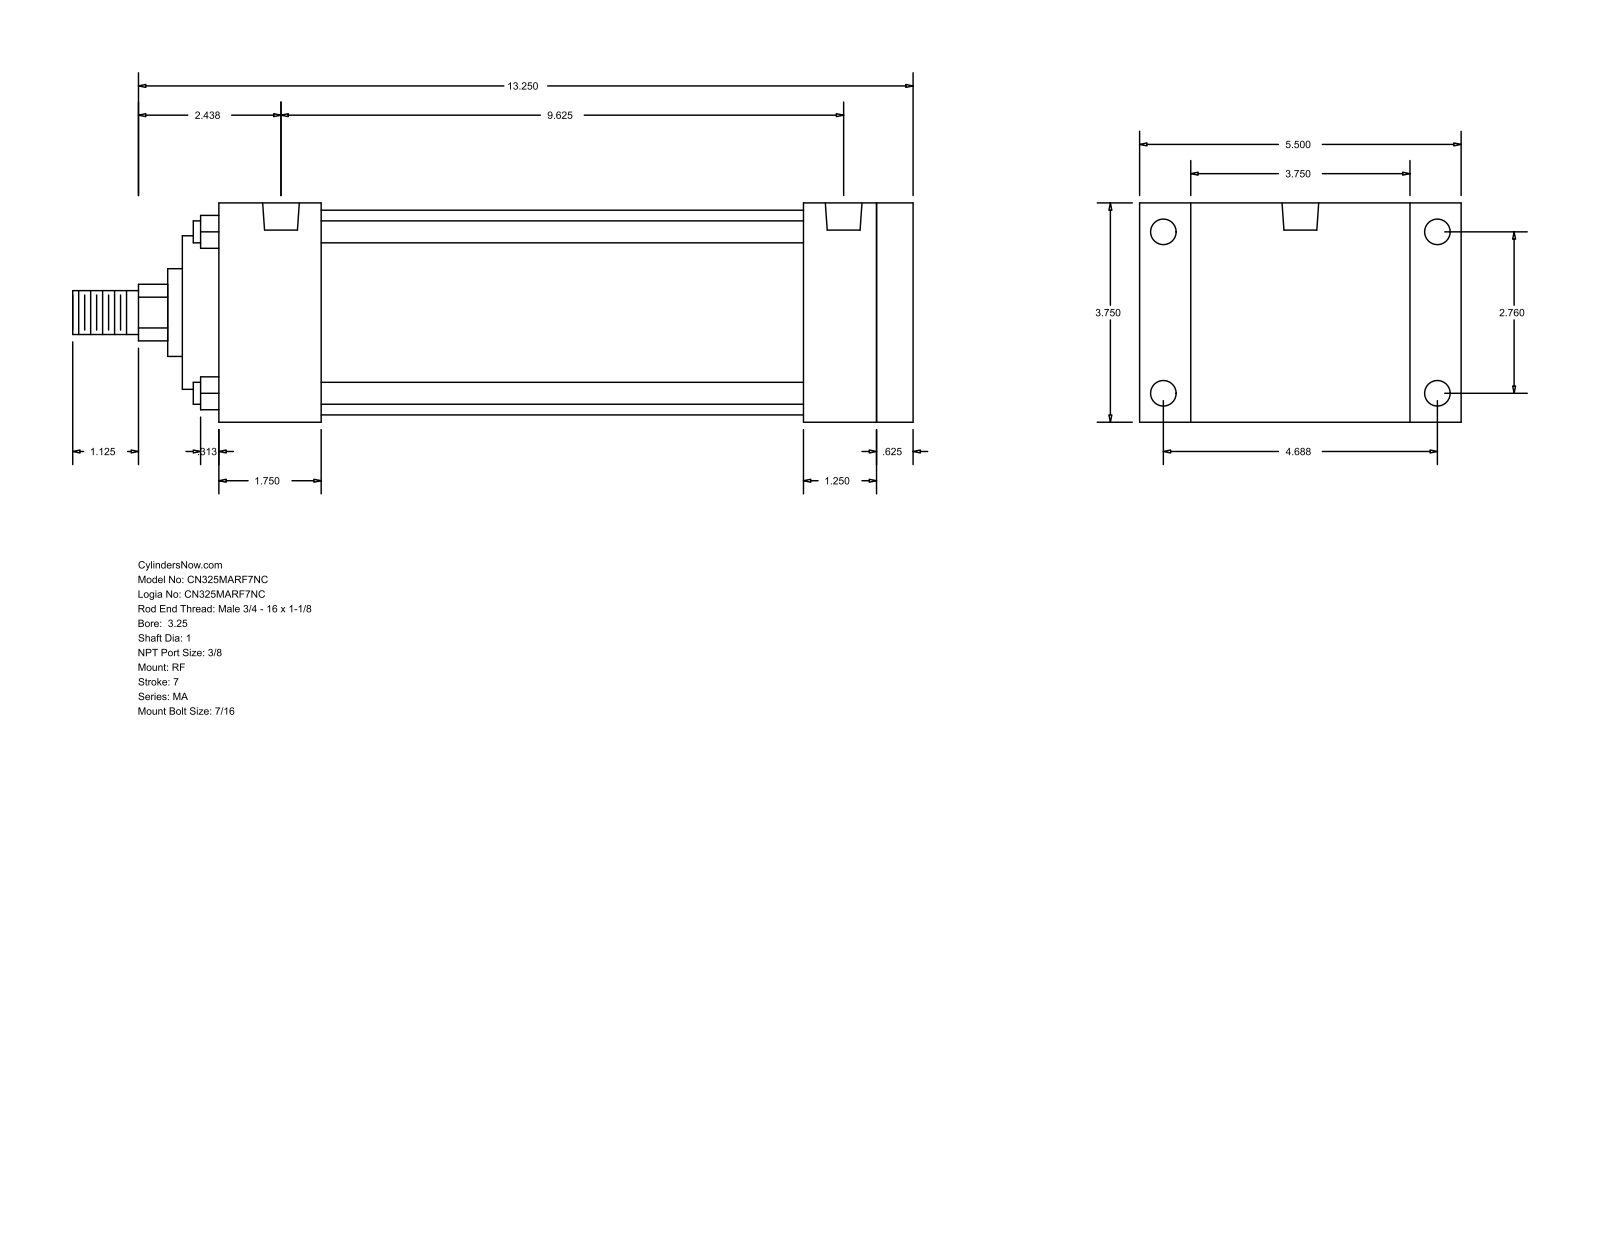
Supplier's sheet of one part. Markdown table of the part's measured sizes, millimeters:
| quantity | value |
| --- | --- |
| part name | MA_RF__0325_1 |
| STEP written by | GSSL Pune (CONFIG_CONTROL_DESIGN) |
| units | millimeters |
| bodies | 0 solids, 94 faces (65 planar, 29 cylindrical, 0 other) |
| overall size | 365.12 × 139.7 × 95.25 |
| round holes (diameter × count) | 11.11 × 8, 15.93 × 2 |
| round bosses / shafts (diameter × count) | 9.53 × 4, 88.9 × 1, 66.67 × 1, 38.1 × 1, 25.4 × 1, 19.05 × 1 |
| partial cylindrical surfaces (radius × count) | 12.29 × 1 |
| main face-to-face distances | 95.24, 301.63, 15.87, 285.76, 22.23, 117.47, 47.62, 317.5, 254.01, 31.75 |
| hole center spacings | 70.1, 119.06, 138.16, 234.95, 4.76, 4.77, 239.71, 239.72 |
